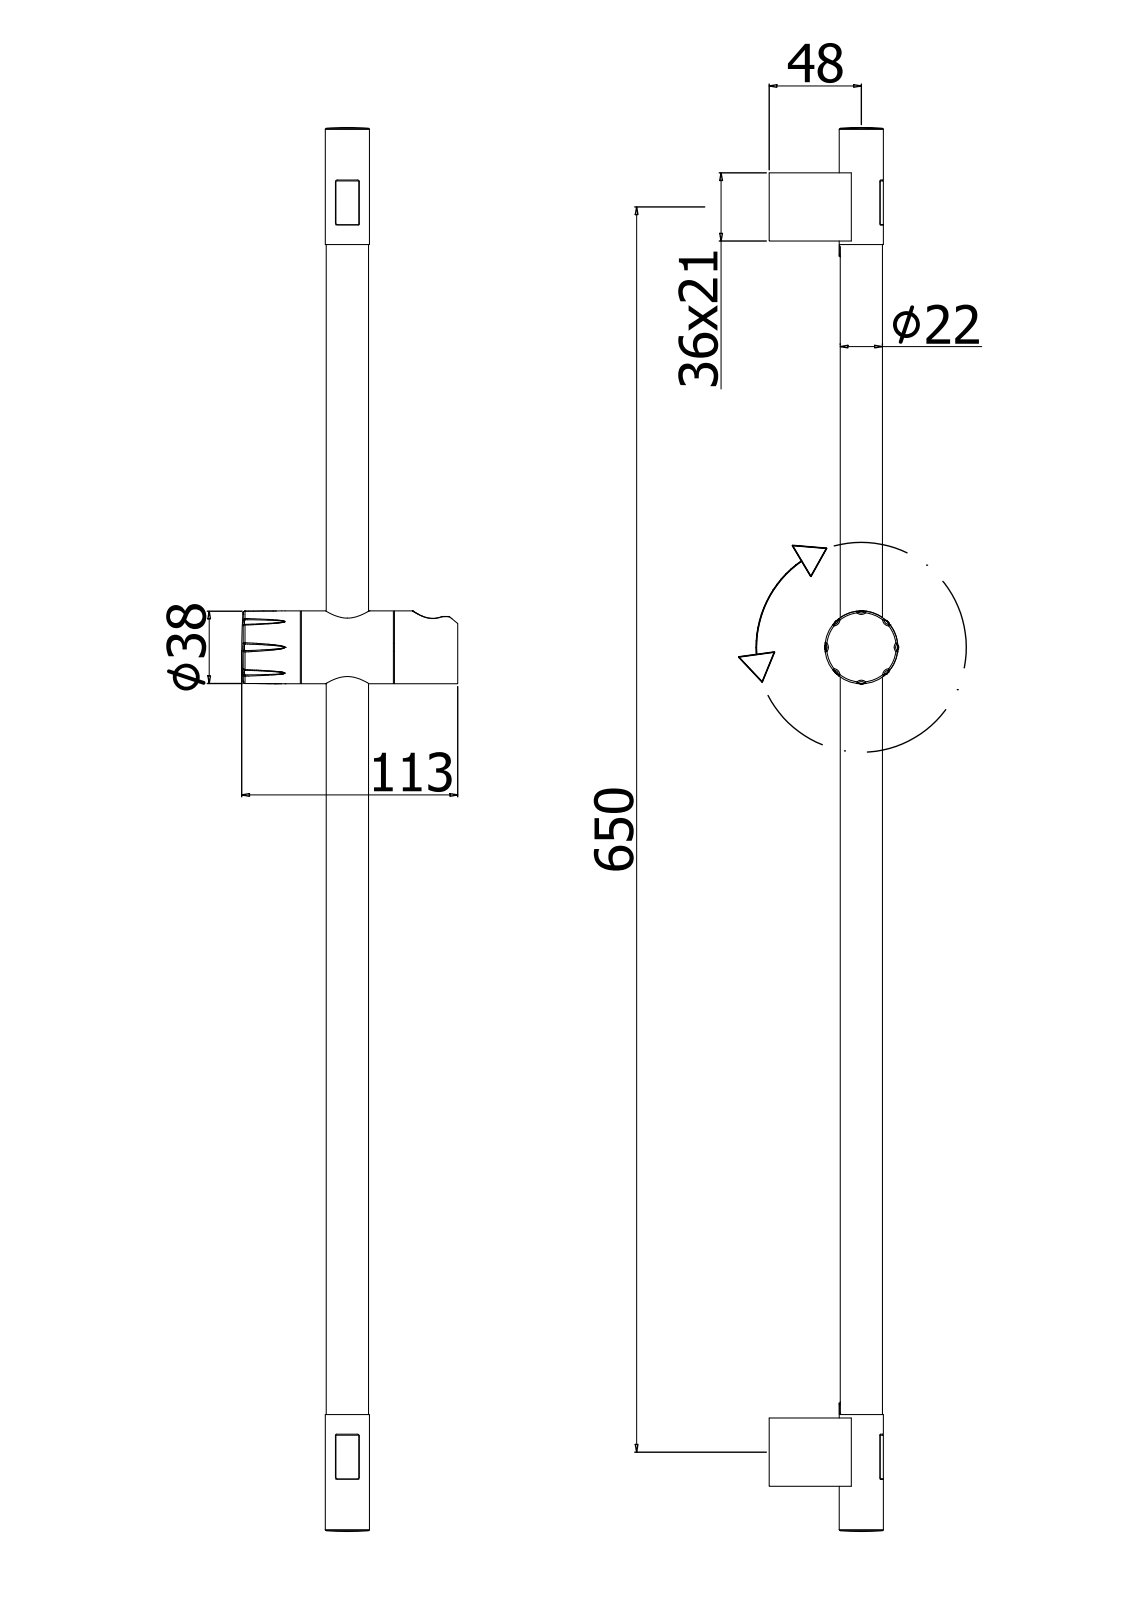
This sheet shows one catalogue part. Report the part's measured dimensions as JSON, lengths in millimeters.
{"part_name": "ZSAL108CR", "step_written_by": "CREO PARAMETRIC BY PTC INC, 2020044 (CONFIG_CONTROL_DESIGN)", "units": "millimeters", "bodies": {"solids": 4, "faces": 1114, "planar": 340, "cylindrical": 275, "other": 499}, "overall_size": [706, 182.32, 89.26], "volume_mm3": 173932, "surface_area_mm2": 198413, "round_holes": [[9.3, 1], [12, 1], [21, 1], [22.2, 1], [35.1, 1]], "round_bosses_or_shafts": [[3, 8], [37.1, 1], [33.1, 1], [32.1, 1], [31.8, 1], [29.8, 1], [26.9, 1], [26, 1]], "partial_cylinders_radius": [[1, 54], [0.5, 20], [0.78, 4], [1.35, 4], [1.42, 4], [1.85, 4], [2, 4], [5, 4]], "face_to_face_distances": [12.5, 2.5, 2, 10, 3.5, 13.5, 16, 1, 1.5, 45.7], "hole_center_spacings": [69]}
